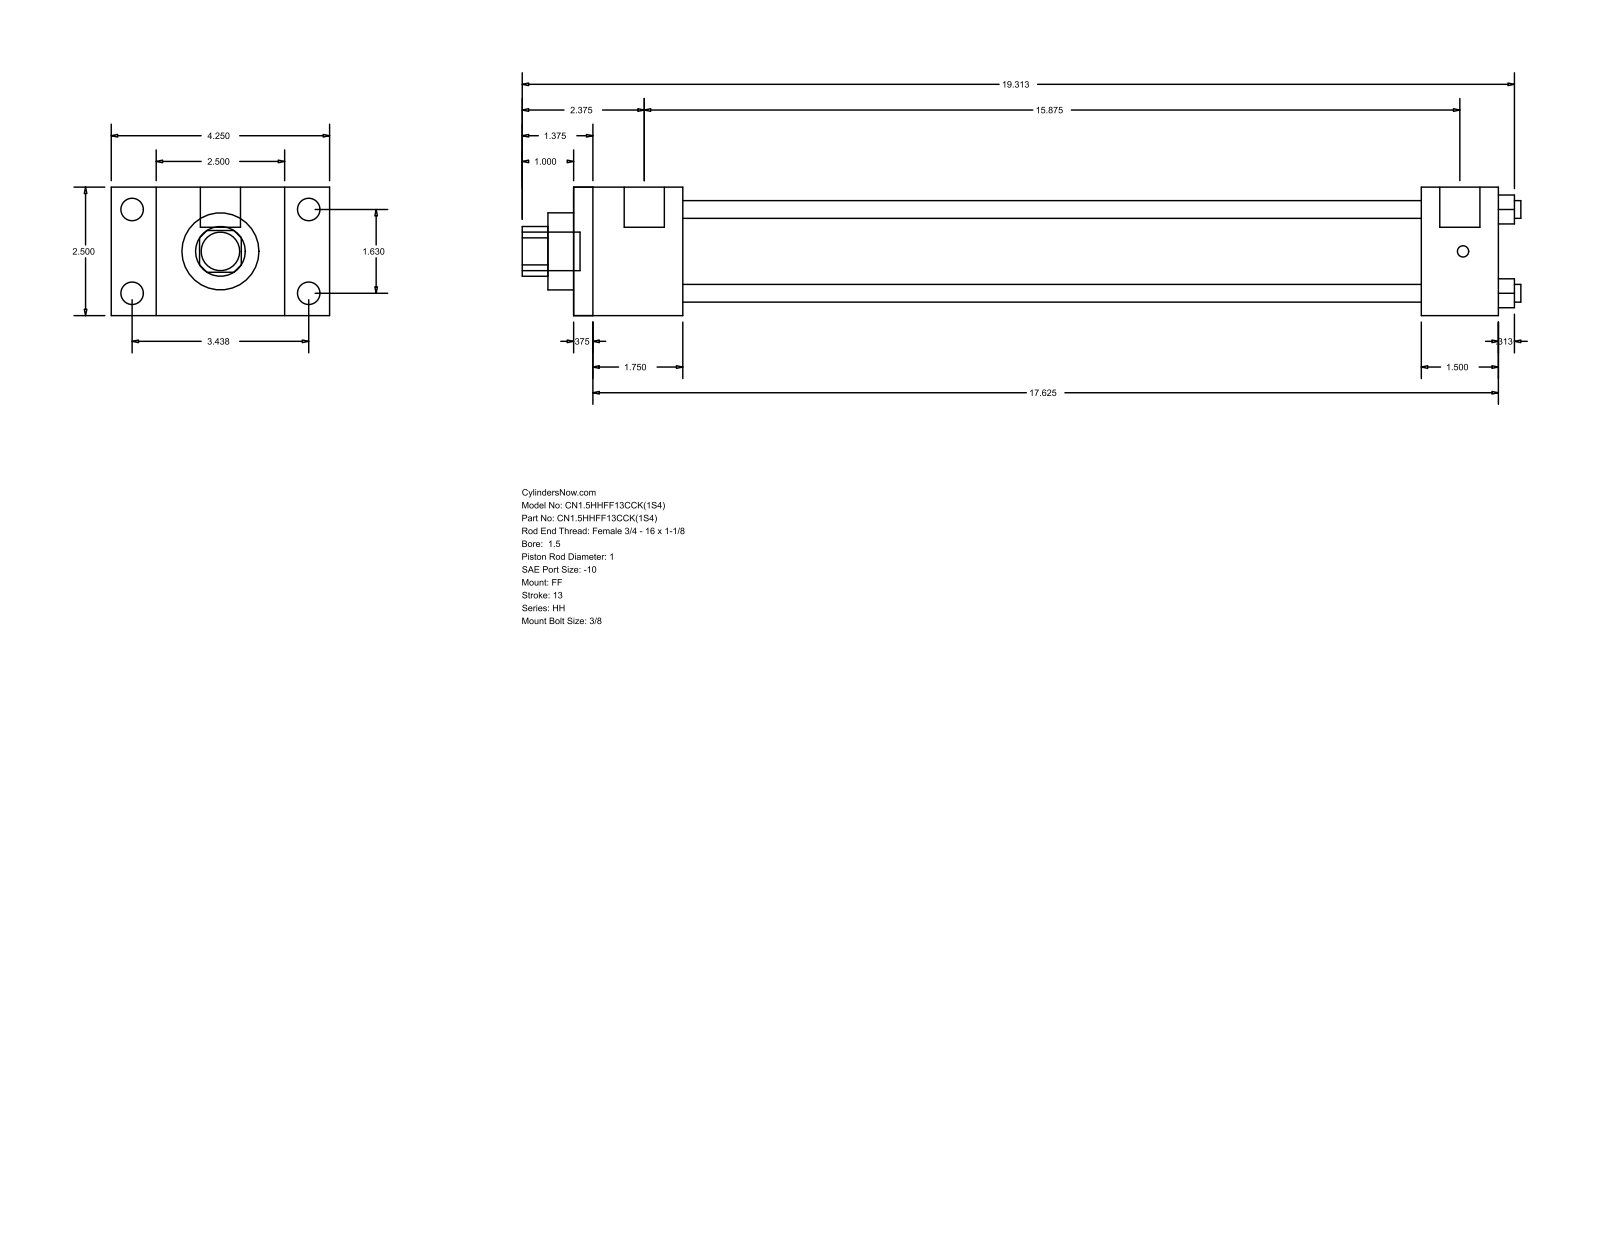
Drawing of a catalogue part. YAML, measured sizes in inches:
part_name: "HH_FF__0150_1"
step_written_by: "GSSL Pune (CONFIG_CONTROL_DESIGN)"
units: inches
bodies: {solids: 0, faces: 92, planar: 64, cylindrical: 28, other: 0}
overall_size: [19.437, 4.25, 2.5]
round_holes:
  - {diameter: 0.345, count: 4}
  - {diameter: 1, count: 1}
  - {diameter: 1.5, count: 1}
  - {diameter: 1.75, count: 1}
round_bosses_or_shafts:
  - {diameter: 0.438, count: 4}
  - {diameter: 0.219, count: 4}
  - {diameter: 0.781, count: 2}
  - {diameter: 0.75, count: 1}
partial_cylinders:
  - {radius: 0.484, count: 1}
face_to_face_distances: [2.5, 18, 0.375, 17.625, 2.125, 1.75, 15.875, 16.5, 16.125, 14.375]
hole_center_spacings: [1.152, 1.63, 2.305]
